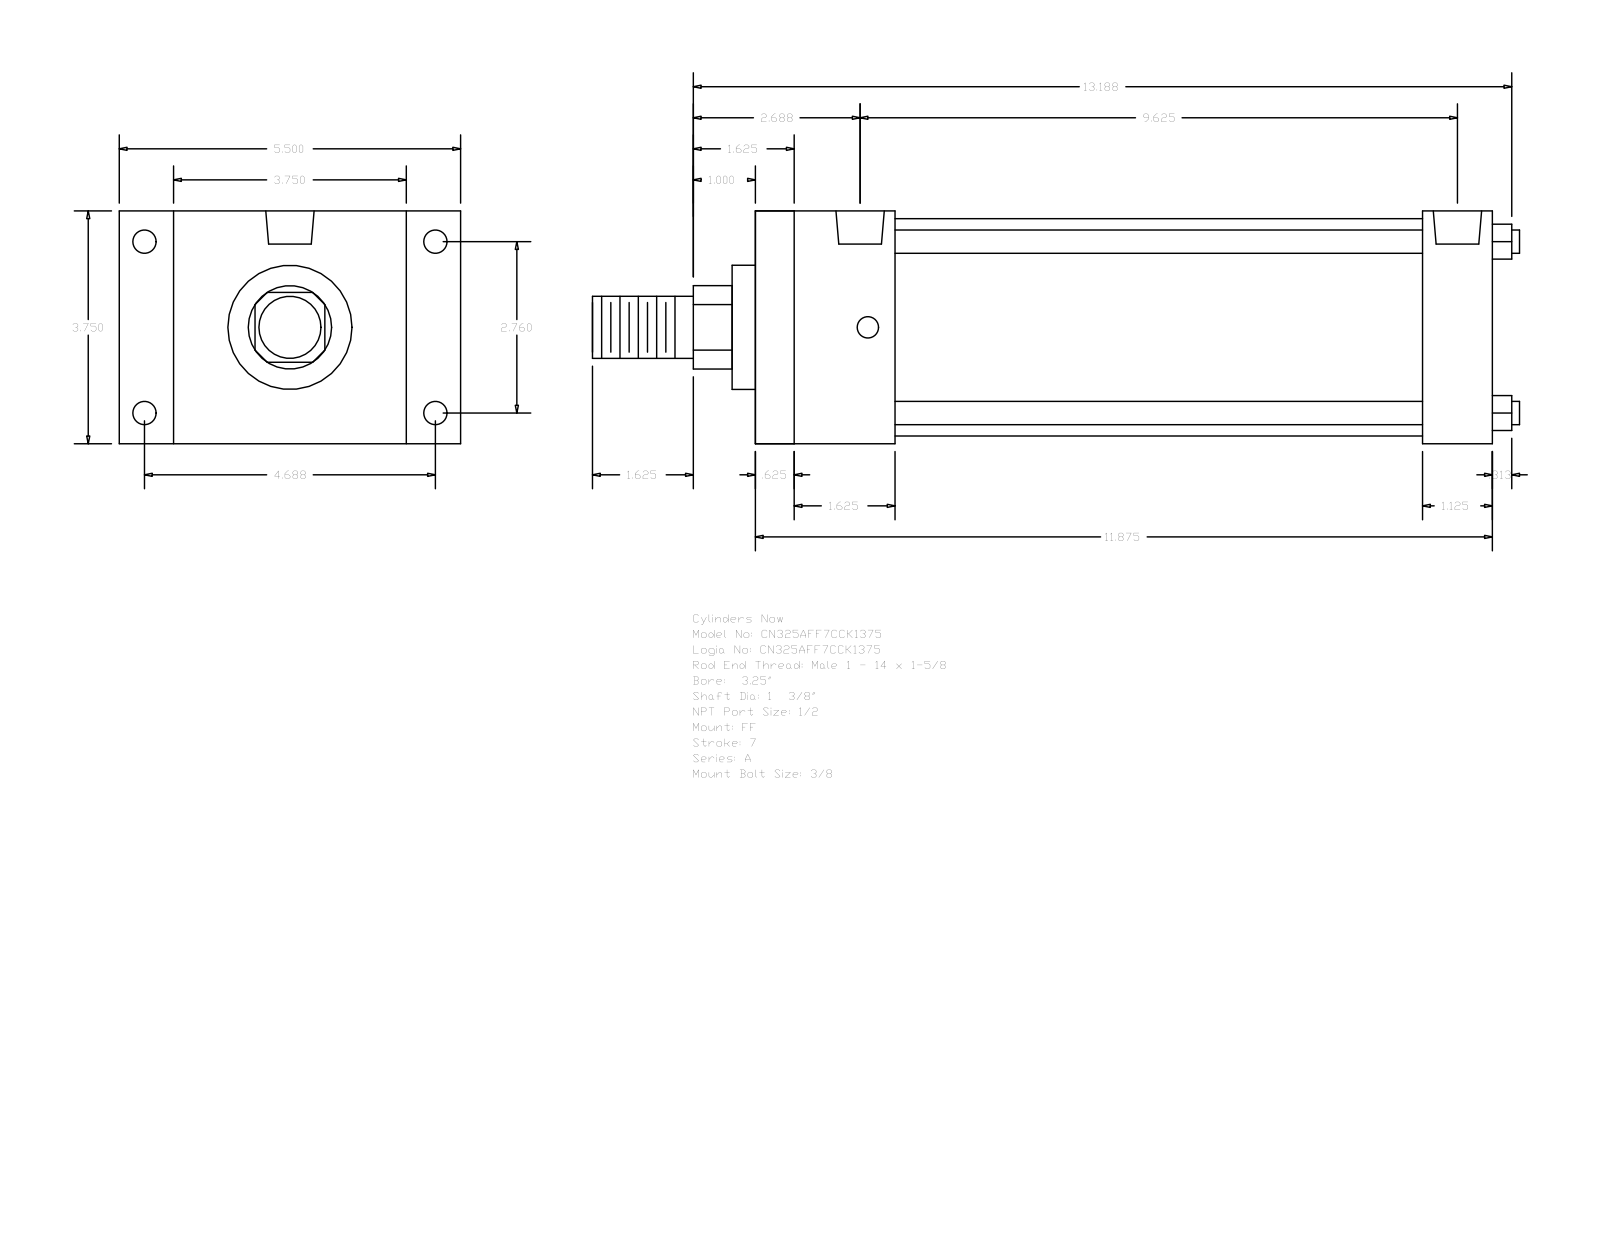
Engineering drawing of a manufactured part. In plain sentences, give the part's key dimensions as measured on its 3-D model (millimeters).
The part is named "A_FF__0325_1.375". Its 3-D file was written by "GSSL Pune (CONFIG_CONTROL_DESIGN)". It is 0 solids with 92 faces: 64 planar, 28 cylindrical and 0 other. Overall it measures 379.41 by 139.7 by 95.25 millimeters. Round holes: 4 of diameter 8.73, 4 of diameter 9.53, 2 of diameter 19.77. Round bosses or shafts: 4 of diameter 9.53, 1 of diameter 88.9, 1 of diameter 50.8, 1 of diameter 34.92, 1 of diameter 25.4. Partial cylindrical surfaces (rounded edges, fillets, slot ends): 1 of radius 17.06. The main face-to-face distances are 95.24, 301.62, 285.75, 15.87, 57.15, 22.23, 117.47, 28.57, 273.05, 41.28. The hole center spacings are 3.18, 70.1, 119.06, 138.16, 238.12, 241.3, 244.48.
